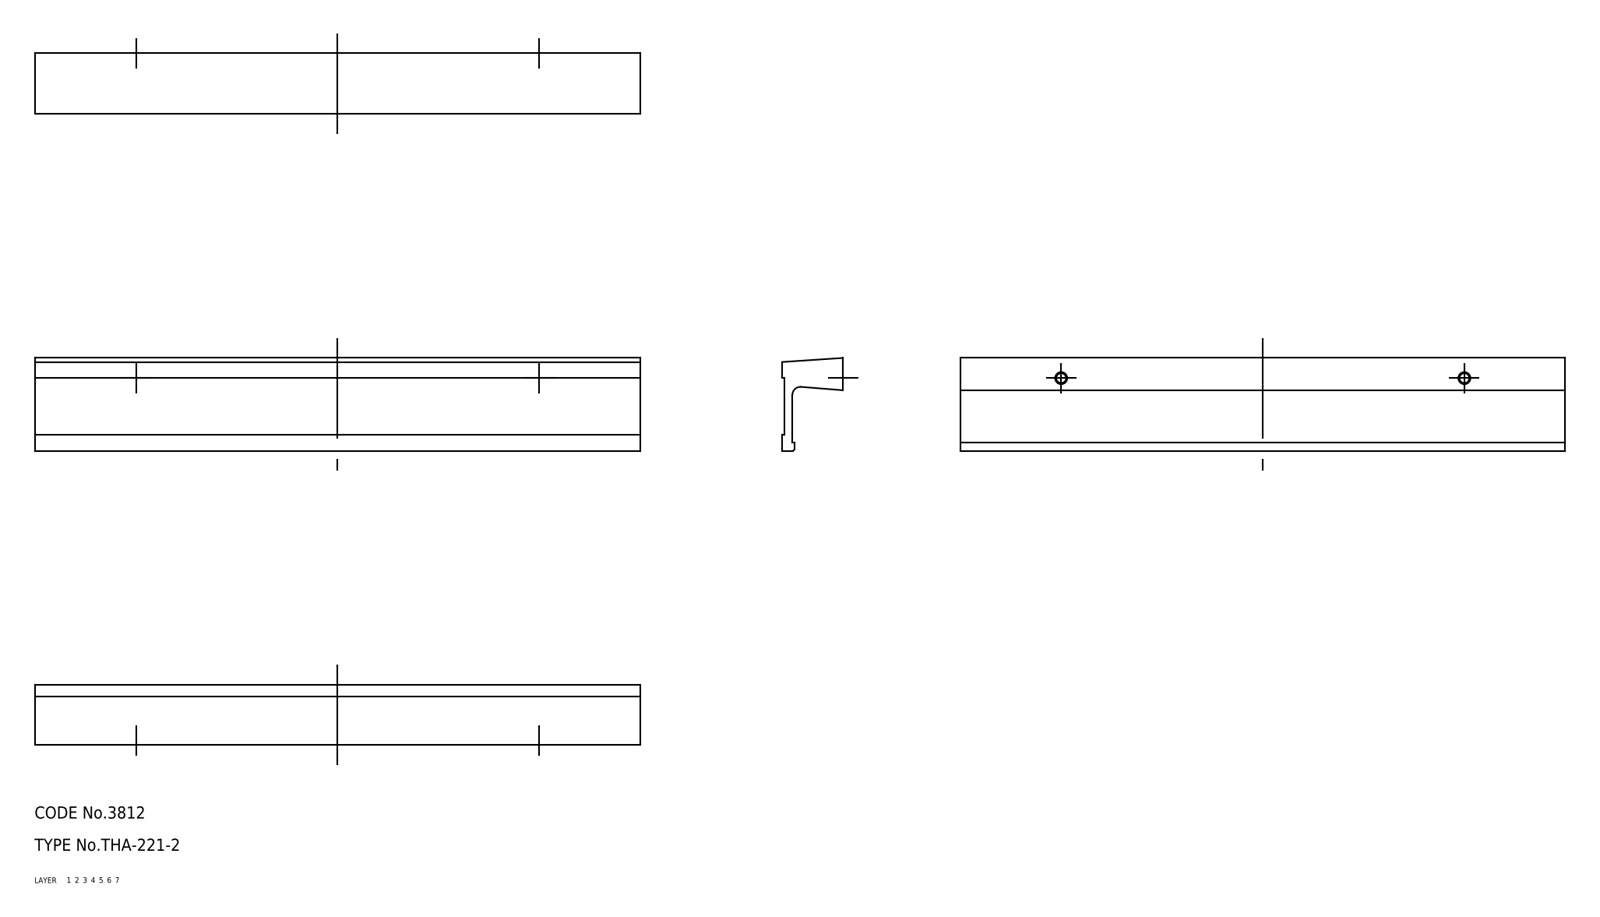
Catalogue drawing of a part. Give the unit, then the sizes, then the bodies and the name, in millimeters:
Units: millimetres
Overall size (bounding box): 150 × 23 × 15
Volume: 20 669 mm³ · Surface area: 11 996 mm²
Bodies: 1 solid, 22 faces (0 planar, 0 cylindrical, 22 other)
Part name (STEP PRODUCT): pull
STEP written by: CADfix (AUTOMOTIVE_DESIGN)
